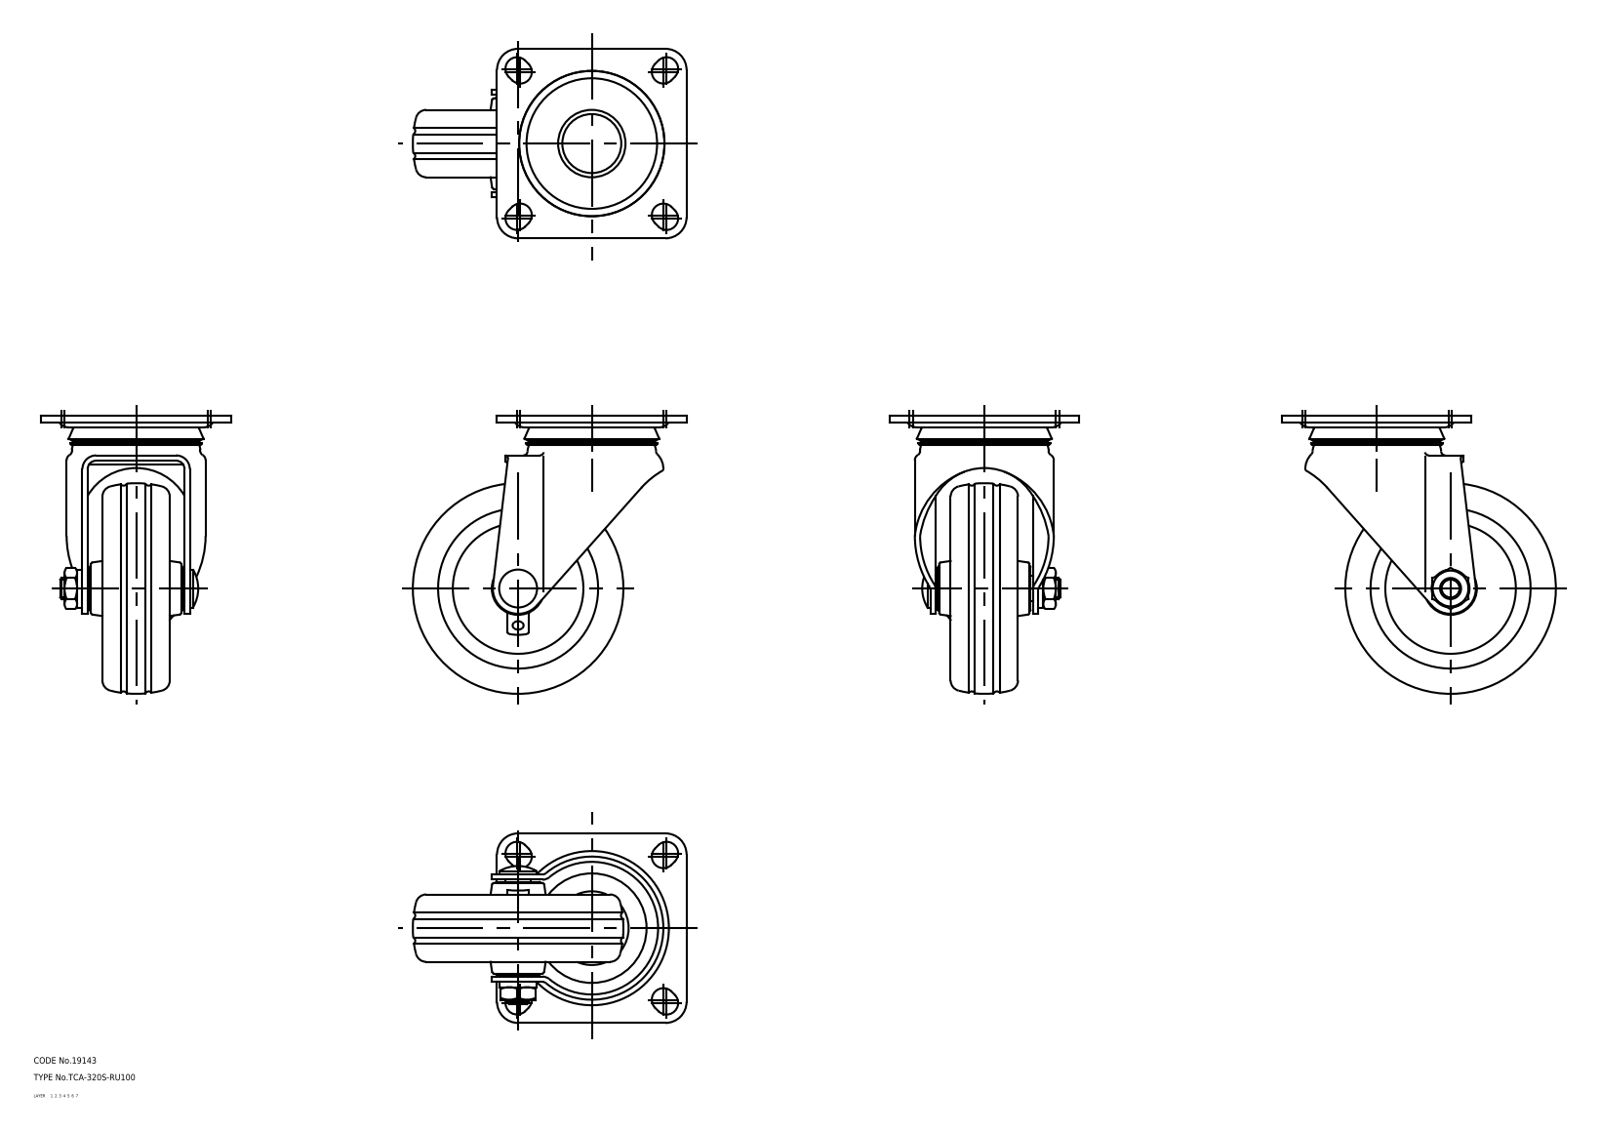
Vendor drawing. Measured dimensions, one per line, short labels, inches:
name: 67128256; 67128269; 67128282; 67128295 (+1 more)
written by: CADfix (AUTOMOTIVE_DESIGN)
unit: in
bodies: 5 solids, 263 faces (0 planar, 0 cylindrical, 263 other)
size: 5.197 × 5.118 × 3.543
volume: 18.53 in³; area: 125.6 in²
